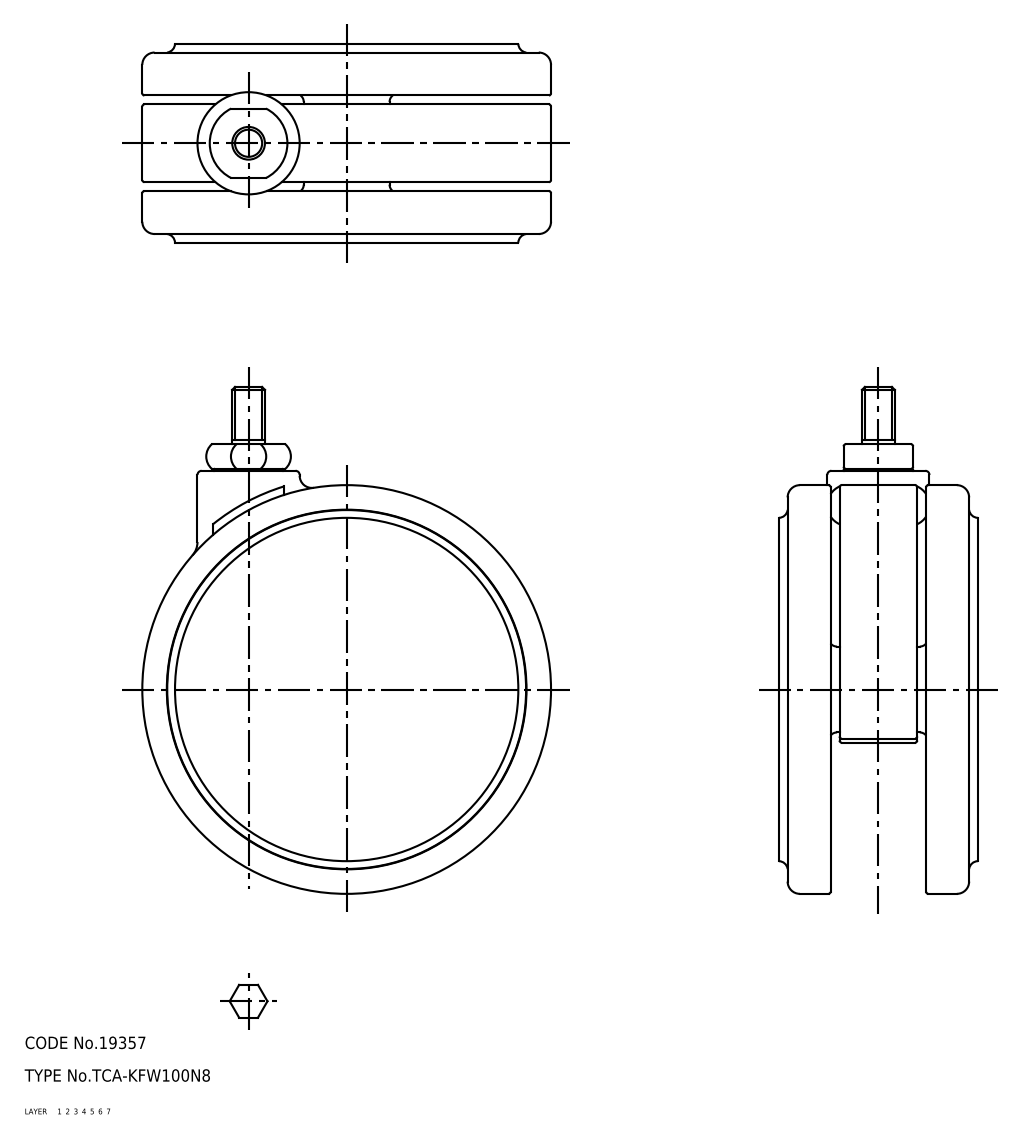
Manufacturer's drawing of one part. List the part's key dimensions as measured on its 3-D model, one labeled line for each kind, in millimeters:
Part name (STEP PRODUCT): caster; TCA-KFW100N8
STEP written by: SolidWorks 2015 (AUTOMOTIVE_DESIGN)
Units: millimetres
Bodies: 1 solid, 999 faces (379 planar, 396 cylindrical, 224 other)
Overall size (bounding box): 124 × 100 × 48.6
Volume: 176 151 mm³ · Surface area: 88 890 mm²
Round holes (diameter × count): ⌀7.98 ×1, ⌀8.07 ×1, ⌀9.3 ×1, ⌀10.7 ×1, ⌀12.3 ×1, ⌀13 ×1, ⌀24 ×1, ⌀81 ×1, ⌀88 ×1
Round bosses / shafts (diameter × count): ⌀100 ×1, ⌀87.8 ×1, ⌀25 ×1, ⌀22 ×1, ⌀17 ×1, ⌀10.5 ×1, ⌀8 ×1, ⌀6.5 ×1
Partial cylindrical surfaces — rounded edges, fillets, slot ends (radius × count): R1 ×30, R0.5 ×19, R0.2 ×16, R2 ×10, R1.5 ×9, R3 ×6, R4 ×1, R8 ×1
Main face-to-face distances: 1.8, 45, 46.8, 3.6, 43.2, 7.6, 12.6, 9, 10.8, 36
